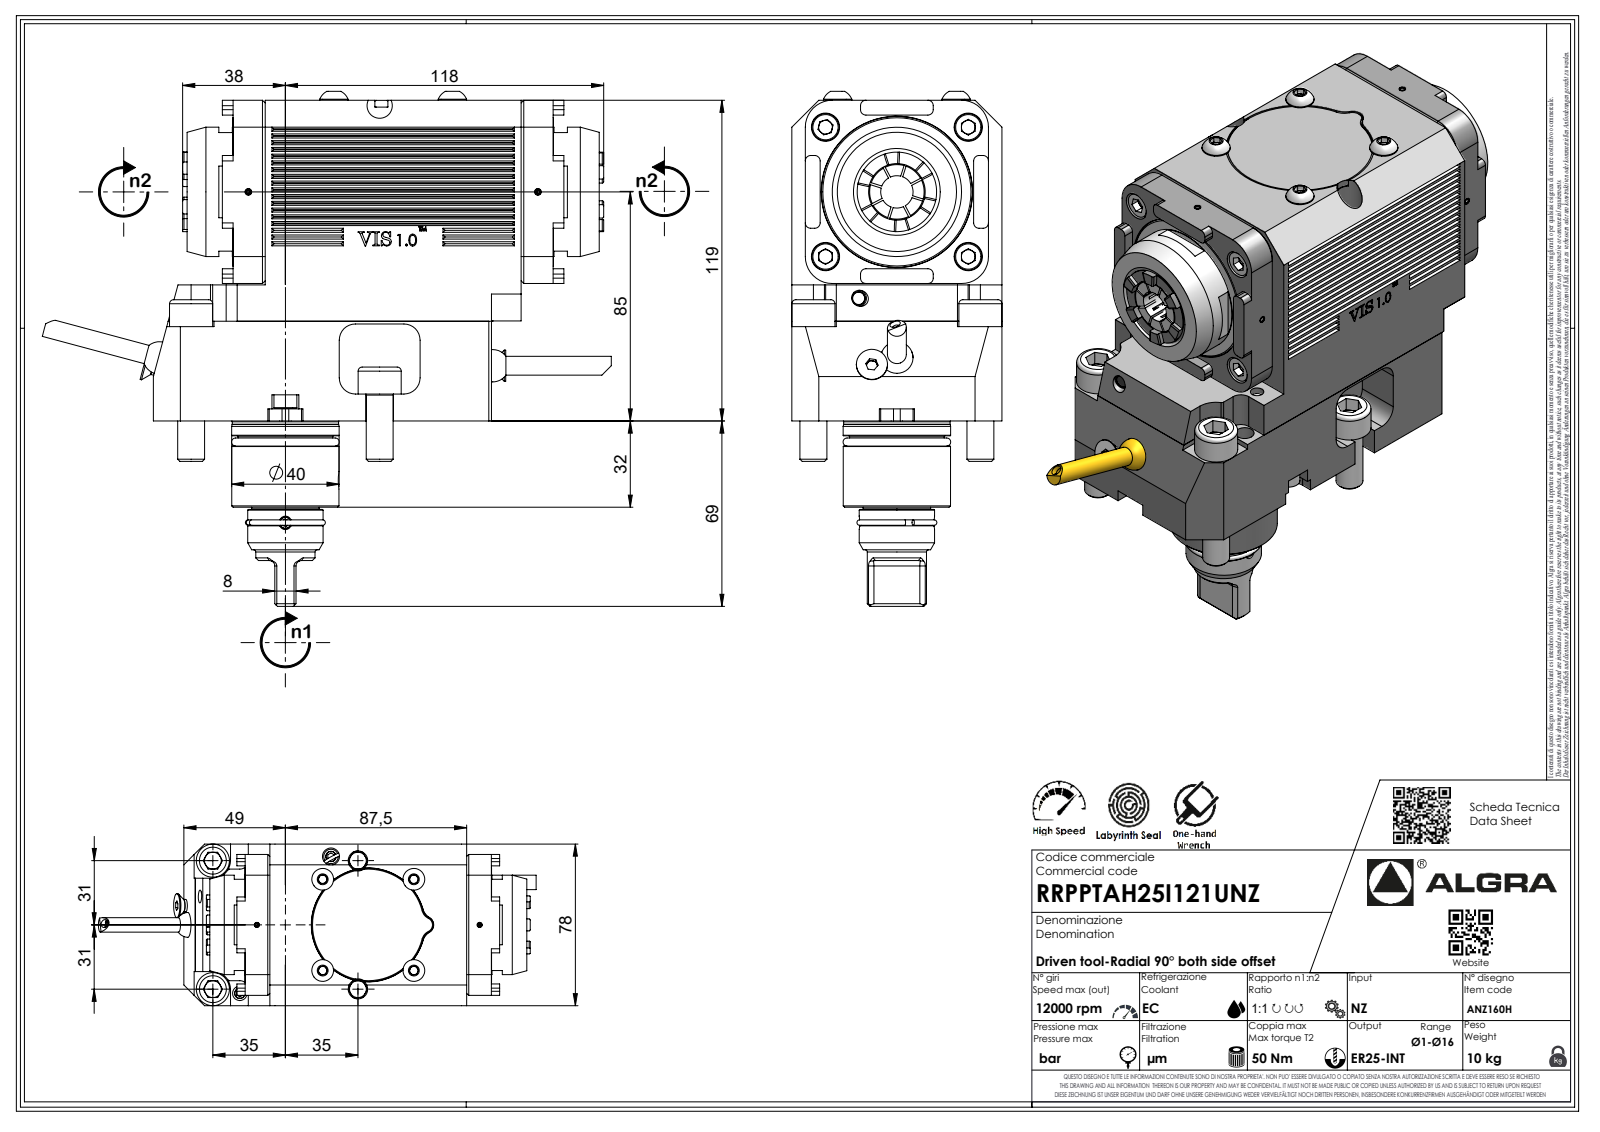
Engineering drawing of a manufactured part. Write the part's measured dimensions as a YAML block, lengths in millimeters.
part_name: "RRPPTAH25I121UNZ"
step_written_by: "SolidWorks 2023 (AUTOMOTIVE_DESIGN)"
units: millimeters
bodies: {solids: 1, faces: 579, planar: 373, cylindrical: 110, other: 96}
overall_size: [211.24, 191.1, 78]
volume: 1215000
surface_area: 88087
round_holes:
  - {diameter: 4, count: 2}
  - {diameter: 2.1, count: 1}
round_bosses_or_shafts:
  - {diameter: 10.5, count: 4}
  - {diameter: 10, count: 4}
  - {diameter: 16, count: 2}
  - {diameter: 7, count: 2}
  - {diameter: 48, count: 1}
  - {diameter: 39.9, count: 1}
  - {diameter: 39.8, count: 1}
  - {diameter: 39.5, count: 1}
partial_cylinders:
  - {radius: 2, count: 24}
  - {radius: 0.33, count: 7}
  - {radius: 0.52, count: 7}
  - {radius: 3.7, count: 7}
  - {radius: 10, count: 4}
  - {radius: 1, count: 2}
  - {radius: 4.1, count: 2}
  - {radius: 8.5, count: 2}
face_to_face_distances: [78, 119, 17.1, 135.9, 5, 50.5, 73, 68, 11.9, 106.9]
